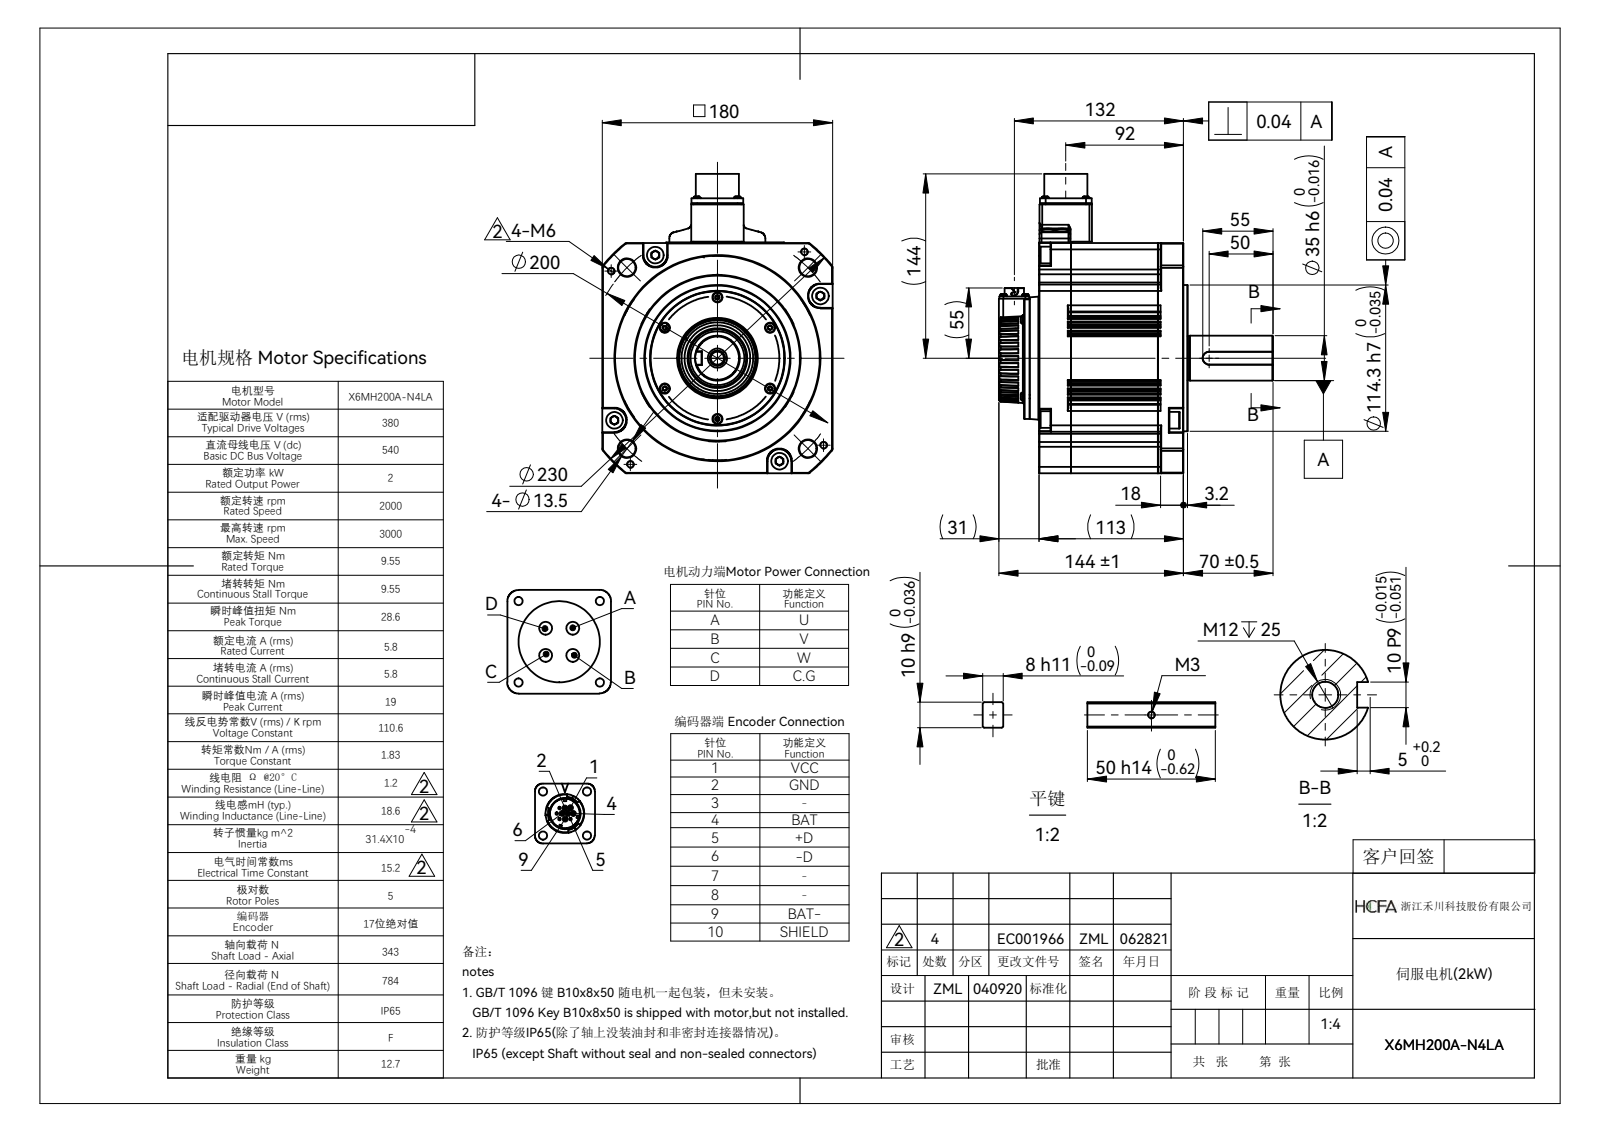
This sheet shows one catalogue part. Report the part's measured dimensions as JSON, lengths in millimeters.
{"part_name": "SV-X2MH200A-N4LA", "step_written_by": "SolidWorks 2016 (CONFIG_CONTROL_DESIGN)", "units": "millimeters", "bodies": {"solids": 1, "faces": 2570, "planar": 835, "cylindrical": 1113, "other": 622}, "overall_size": [233.9, 214.2, 180], "volume_mm3": 3488000, "surface_area_mm2": 201999, "round_holes": [[13.5, 4], [2.5, 2], [5.5, 1], [10.2, 1], [11.6, 1], [11.8, 1], [27.7, 1]], "round_bosses_or_shafts": [[1, 10], [13, 6], [3, 5], [7, 4], [6.7, 4], [5.7, 4], [5, 4], [2.5, 4]], "partial_cylinders_radius": [[0.5, 86], [0.15, 48], [1.5, 43], [1, 40], [0.2, 34], [2, 28], [5, 25], [0.55, 16]], "face_to_face_distances": [180, 32.5, 113, 147.5, 116.2, 3.2, 4, 115, 109, 7.2], "hole_center_spacings": [100, 141.42, 12.16, 49.55, 200, 17.2, 40.2]}
